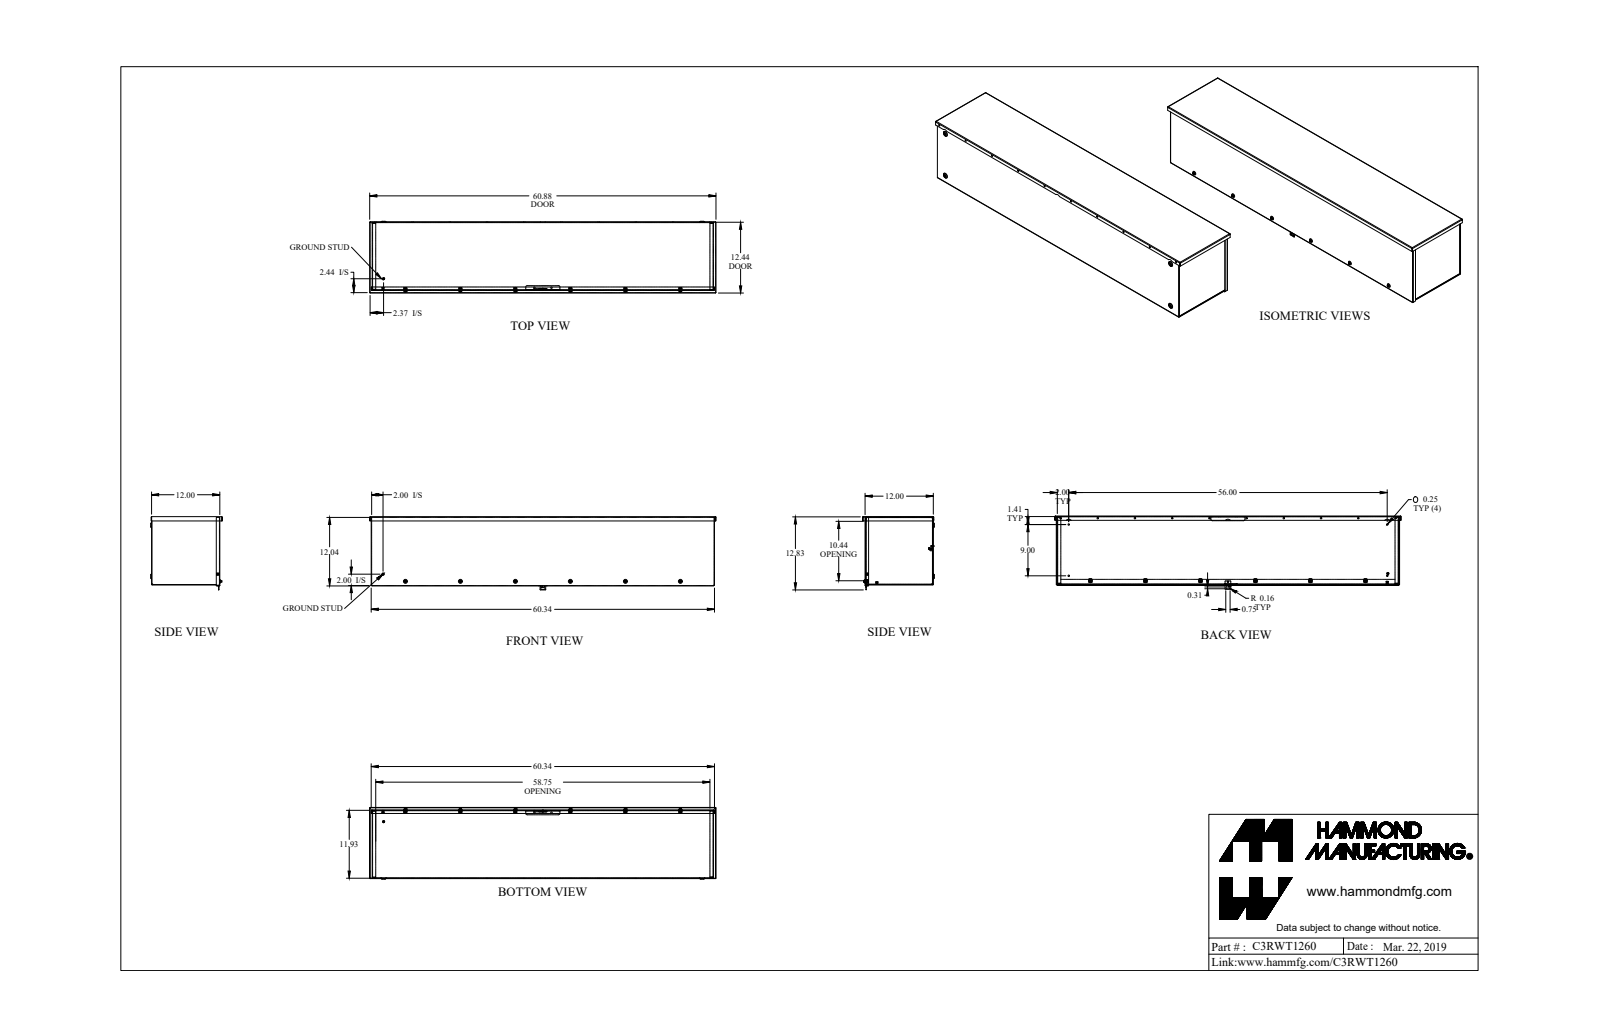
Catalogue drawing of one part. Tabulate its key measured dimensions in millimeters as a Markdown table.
| quantity | value |
| --- | --- |
| part name | C3RWT1260_Default |
| STEP written by | SolidWorks 2019 (CONFIG_CONTROL_DESIGN) |
| units | millimeters |
| bodies | 32 solids, 1166 faces (637 planar, 377 cylindrical, 152 other) |
| overall size | 1546.2 × 326.9 × 319.9 |
| volume | 4 062 000 mm³ |
| surface area | 4 479 000 mm² |
| round holes (diameter × count) | 6.4 × 16, 4 × 8, 5.4 × 6, 5.8 × 6, 5.2 × 2, 3.2 × 1, 3.5 × 1, 5.1 × 1, 5.5 × 1 |
| round bosses / shafts (diameter × count) | 4.8 × 7, 3.8 × 6, 9.5 × 2, 12.7 × 1, 9.3 × 1, 5.3 × 1, 3.9 × 1, 3.2 × 1 |
| partial cylindrical surfaces (radius × count) | 2 × 24, 2.7 × 24, 0.9 × 18, 2.7 × 18, 3.2 × 14, 0.6 × 12, 4.3 × 6, 5.2 × 6 |
| main face-to-face distances | 1.8, 303, 304.8, 301.1, 1.8, 301.1, 303, 1522.2, 1524, 1520.3 |
| hole center spacings | 166.2, 245.6, 332.3, 332.3, 498.5, 664.6, 830.8, 997 |
